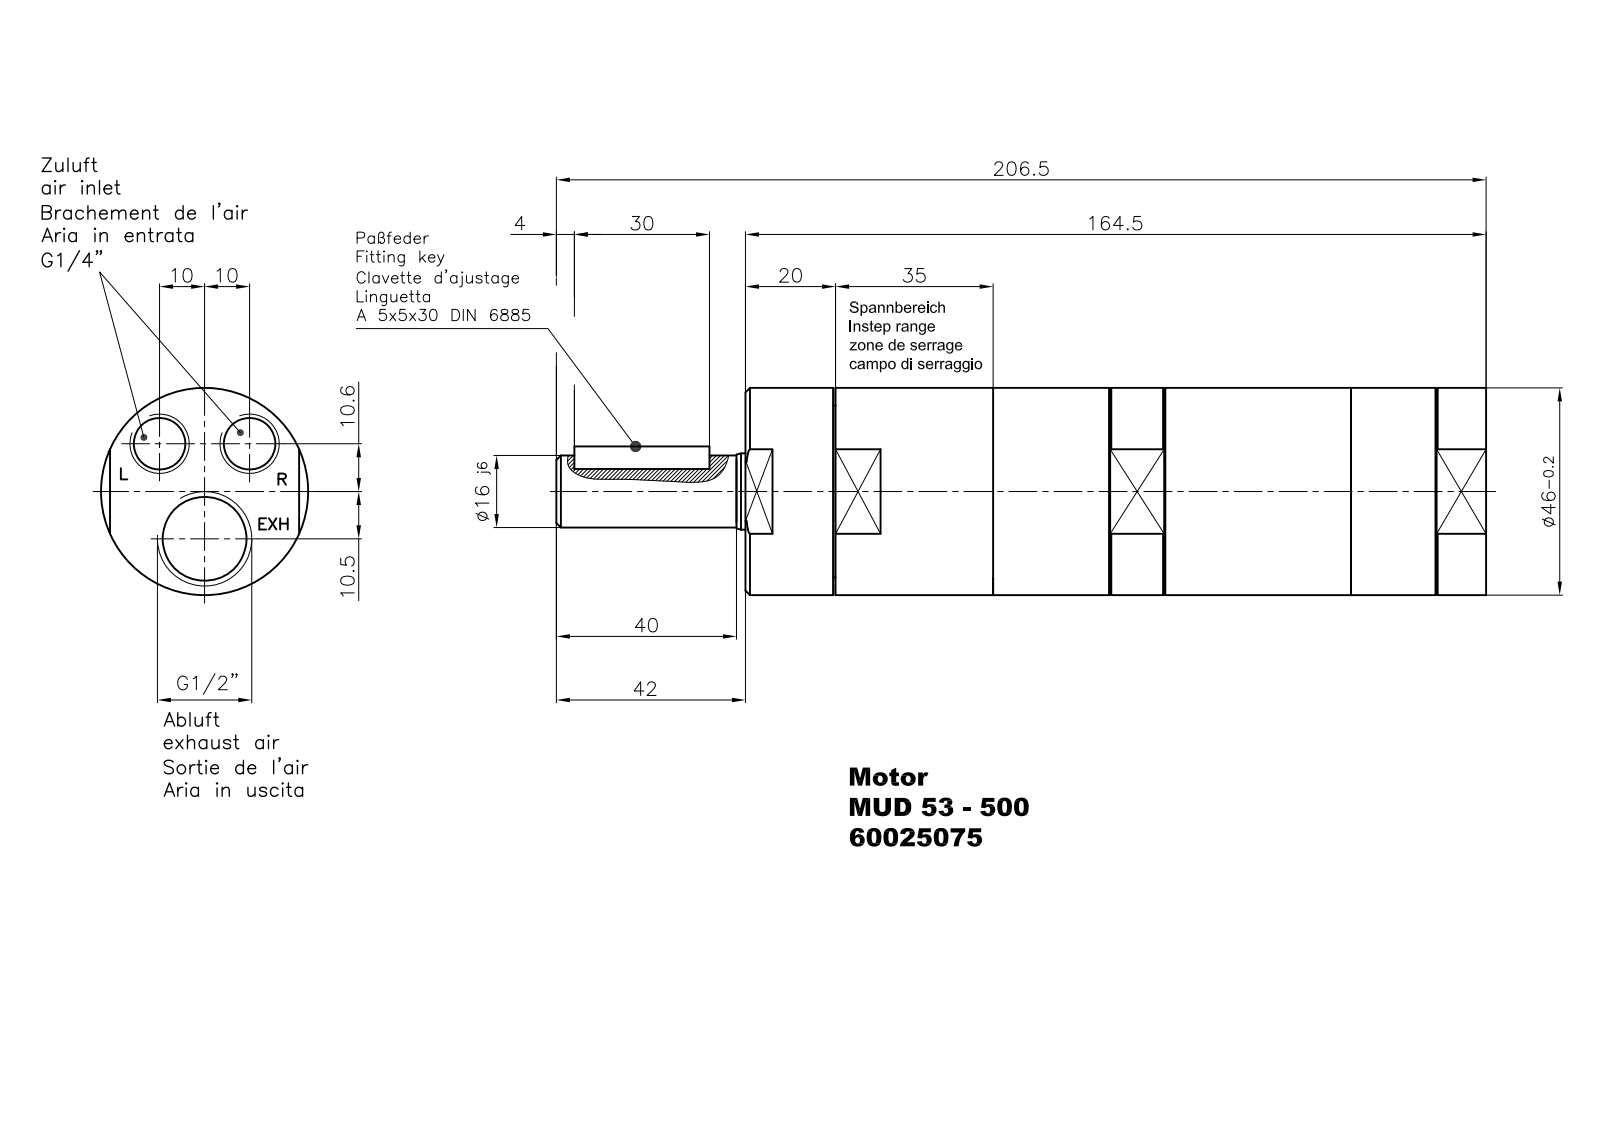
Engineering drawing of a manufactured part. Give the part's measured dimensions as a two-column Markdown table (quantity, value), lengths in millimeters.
| quantity | value |
| --- | --- |
| part name | MUD 53-206 |
| STEP written by | Autodesk Inventor 2012 (AUTOMOTIVE_DESIGN) |
| units | millimeters |
| bodies | 1 solid, 138 faces (94 planar, 19 cylindrical, 25 other) |
| overall size | 206.5 × 46 × 46 |
| volume | 273 349 mm³ |
| surface area | 33 375 mm² |
| round holes (diameter × count) | 11.45 × 2, 1.6 × 1, 17.5 × 1, 18.63 × 1 |
| round bosses / shafts (diameter × count) | 46 × 1, 38.16 × 1, 16.95 × 1, 16 × 1 |
| partial cylindrical surfaces (radius × count) | 2.5 × 2 |
| main face-to-face distances | 164.5, 42, 30, 134.5, 55, 109.5, 79.5, 19.5, 35.5, 115 |
| hole center spacings | 14.57, 23.35, 10.5, 20 |
